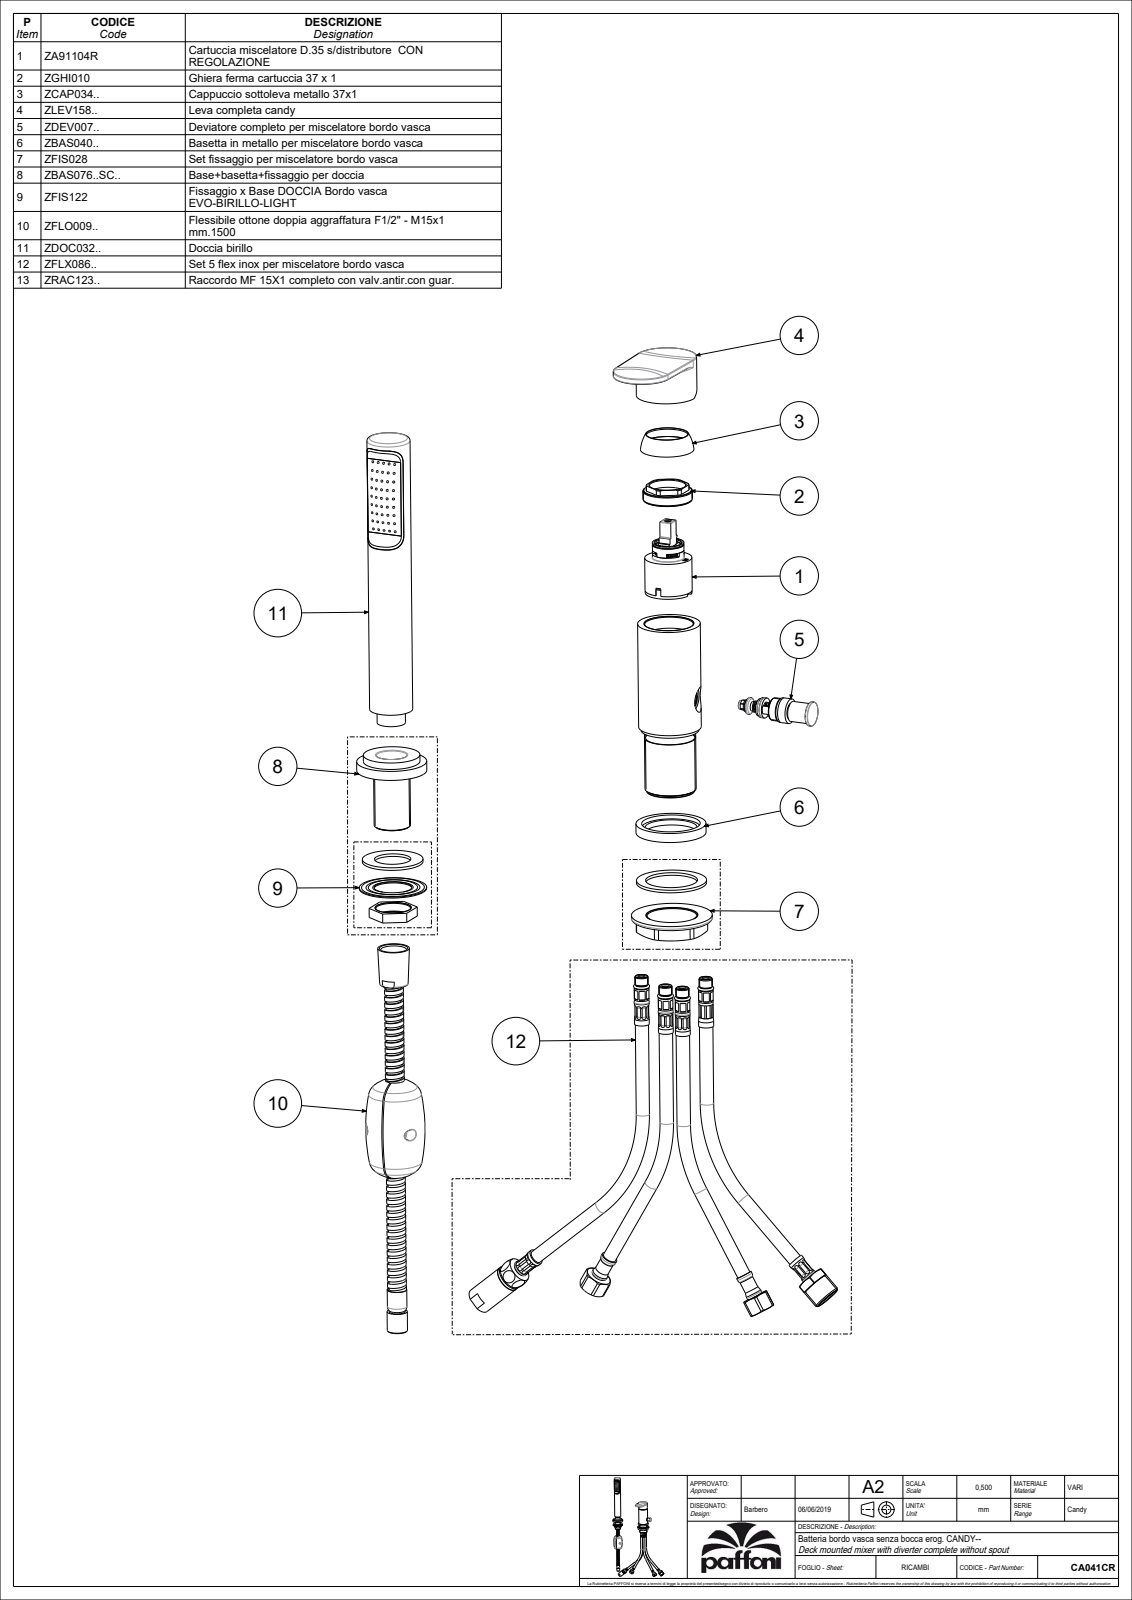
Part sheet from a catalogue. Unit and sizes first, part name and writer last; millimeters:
Units: millimetres
Overall size (bounding box): 237.5 × 218.46 × 88.5
Round holes (diameter × count): ⌀7 ×6, ⌀5 ×2, ⌀3 ×1, ⌀3.5 ×1, ⌀4.5 ×1, ⌀6 ×1, ⌀7.2 ×1, ⌀9 ×1, ⌀9.5 ×1, ⌀13 ×1, ⌀13.5 ×1, ⌀15.2 ×1
Round bosses / shafts (diameter × count): ⌀52 ×2, ⌀46.5 ×1, ⌀45 ×1, ⌀42 ×1, ⌀32 ×1, ⌀21 ×1, ⌀18.5 ×1, ⌀18 ×1
Partial cylindrical surfaces — rounded edges, fillets, slot ends (radius × count): R3 ×4, R3.5 ×1, R8.5 ×1, R21.5 ×1
Main face-to-face distances: 7, 116.6, 109.6, 12, 5, 104.6, 44, 56, 49, 60.6
Hole centre spacings: 3, 8.6, 10.63, 13.45, 14, 14.32, 15.13, 18.11
Volume: 331 689 mm³ · Surface area: 77 230 mm²
Bodies: 4 solids, 267 faces (73 planar, 101 cylindrical, 93 other)
Part name (STEP PRODUCT): CA041CR_SW0001
STEP written by: CREO PARAMETRIC BY PTC INC, 2020044 (CONFIG_CONTROL_DESIGN)
